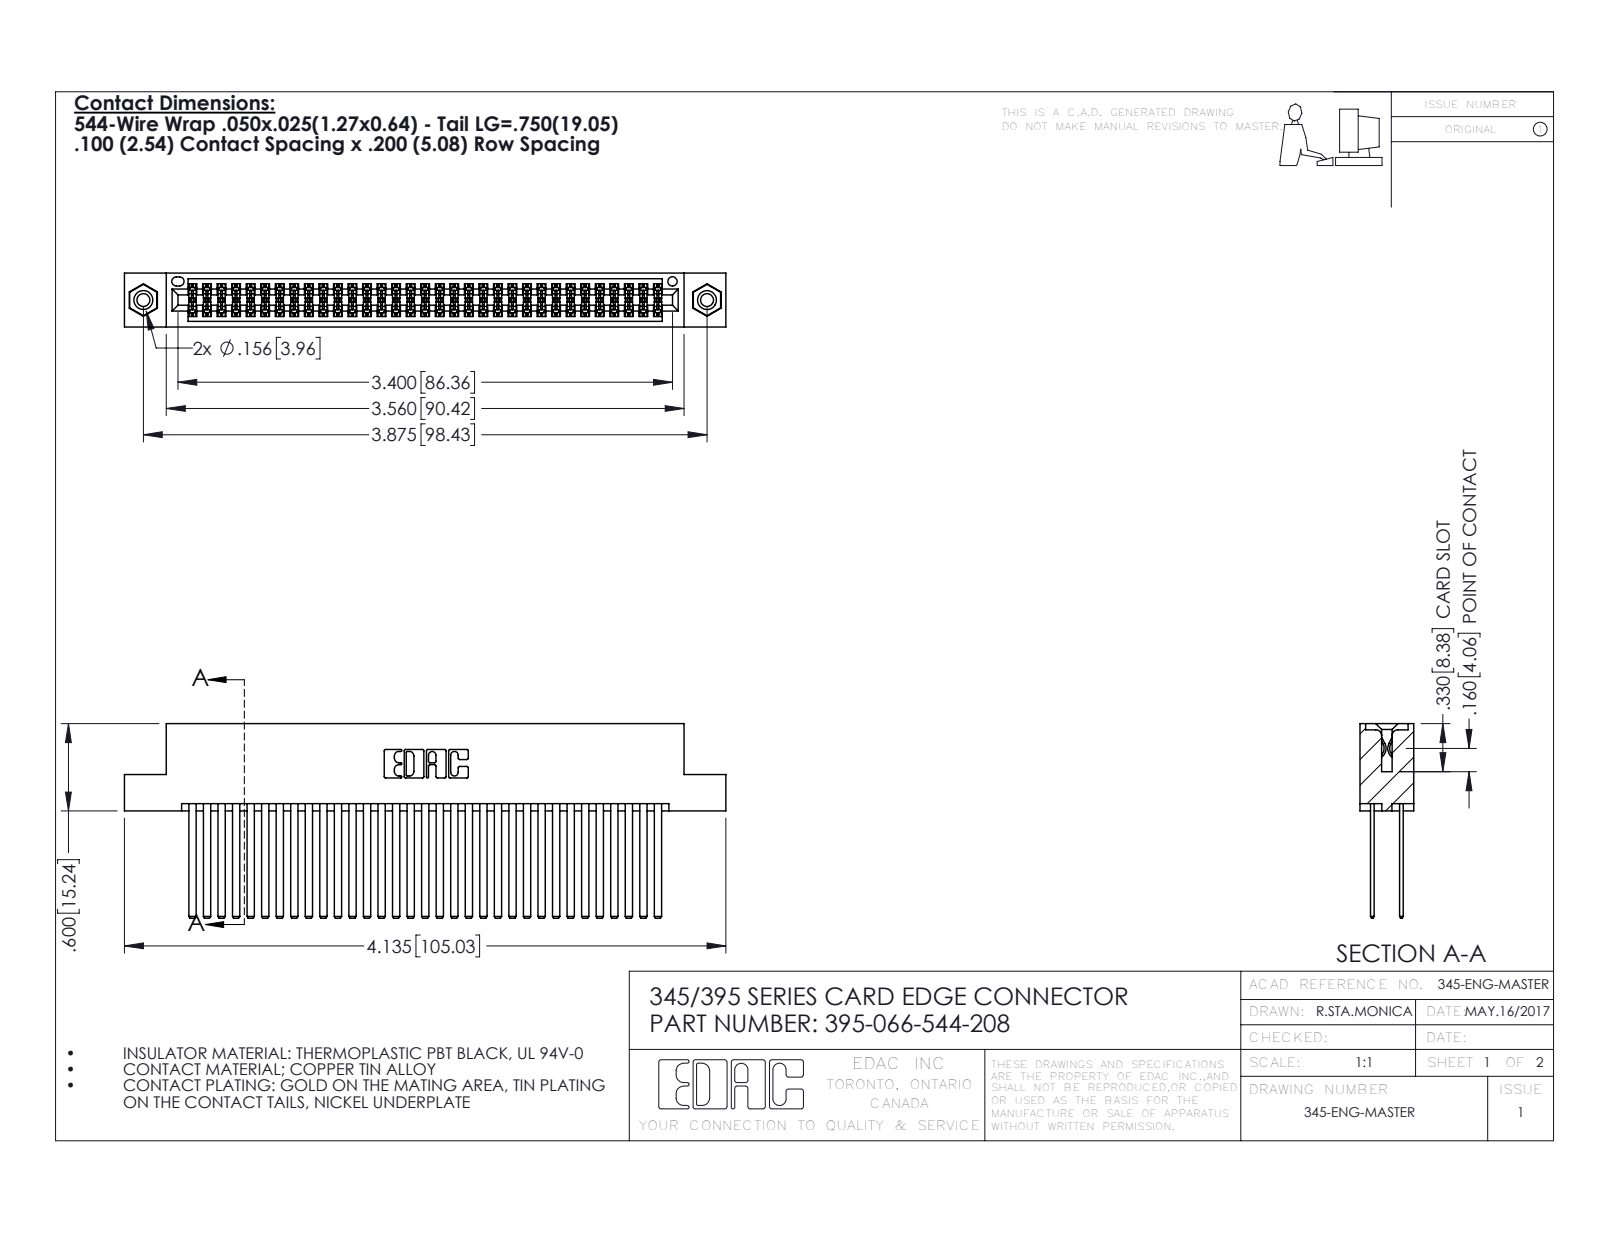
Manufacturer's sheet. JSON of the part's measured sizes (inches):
{"part_name": "395-066-544-208; 345-292-001_345-293-144; 345 Part_Flush Mounting Lugs - 0.156 Dia-TI; 345-250-001_345-250-003-102", "step_written_by": "SolidWorks 2016 (CONFIG_CONTROL_DESIGN)", "units": "inches", "bodies": {"solids": 69, "faces": 3090, "planar": 2026, "cylindrical": 1048, "other": 16}, "overall_size": [4.135, 1.337, 0.37], "volume_in3": 0.674, "surface_area_in2": 29.24, "round_holes": [[0.089, 2], [0.125, 2], [0.156, 2], [0.064, 1]], "round_bosses_or_shafts": [[0.155, 2]], "partial_cylinders_radius": [[0.006, 99], [0.01, 22], [0.007, 6], [0.031, 6], [0.026, 3], [0.014, 2], [0.019, 2], [0.022, 2]], "face_to_face_distances": [0.2, 0.025, 0.072, 0.098, 0.272, 0.298, 0.225, 0.175, 0.37, 0.05], "hole_center_spacings": [0.27, 3.64, 3.875]}
